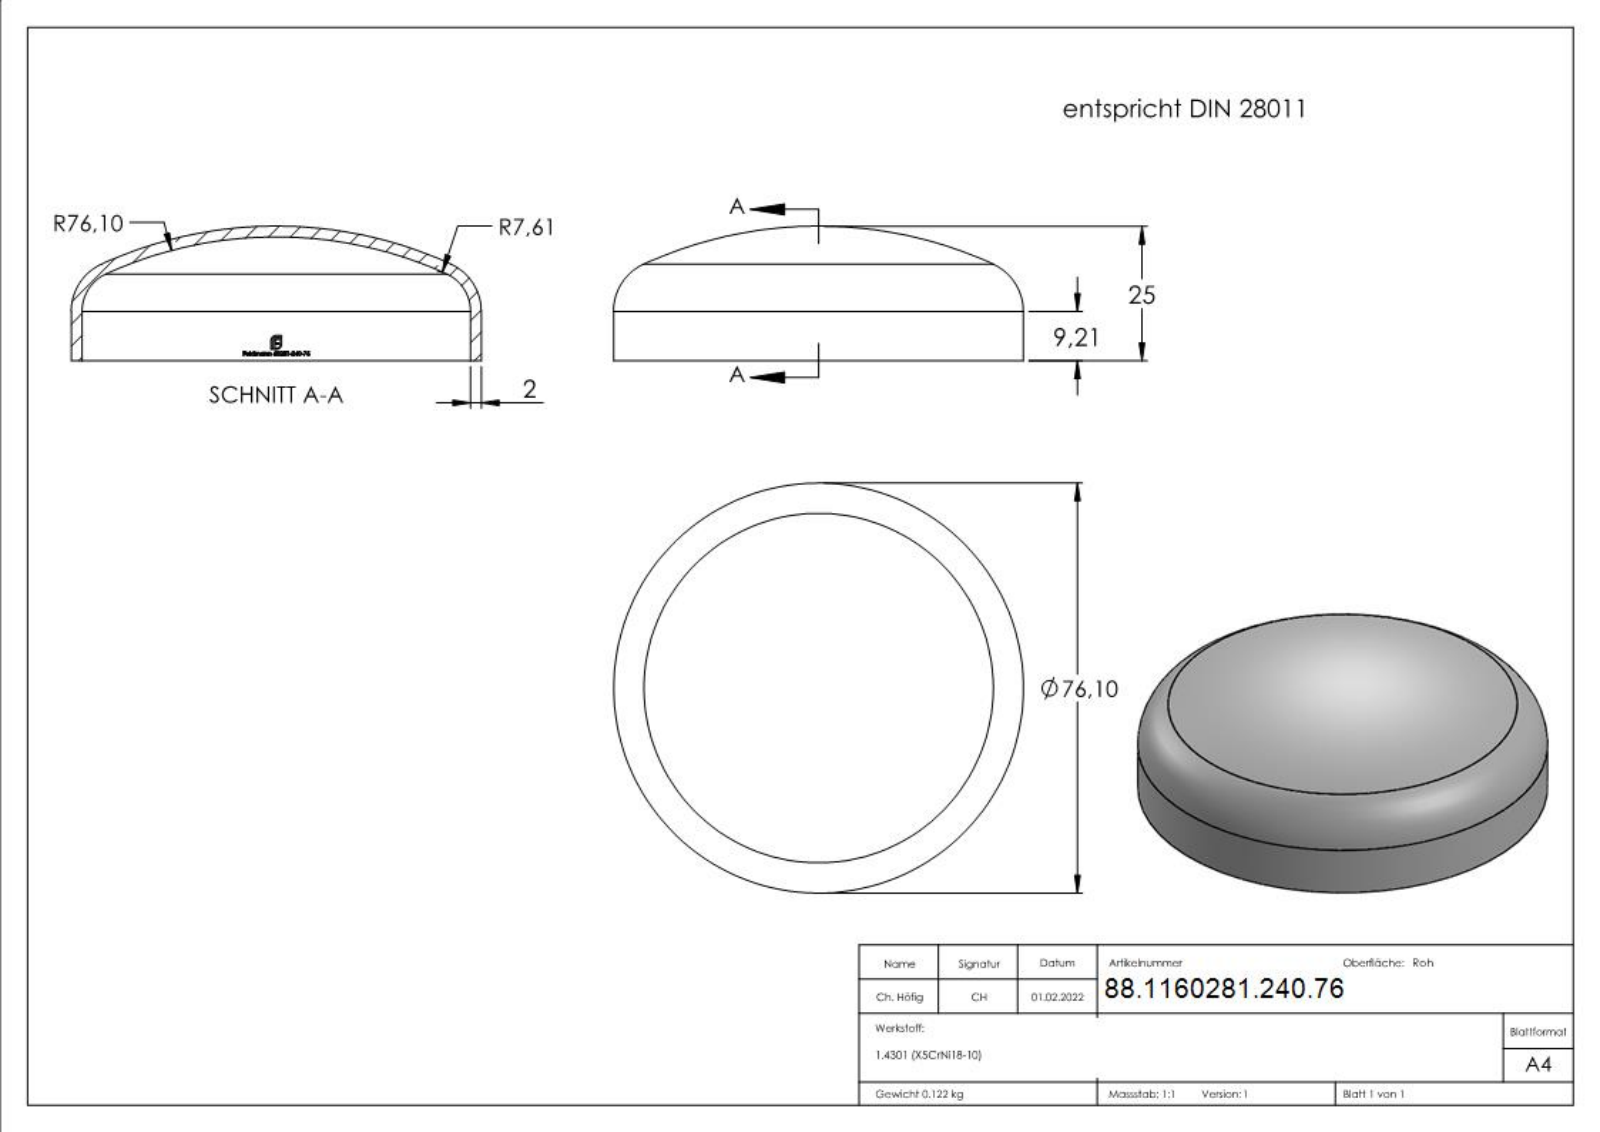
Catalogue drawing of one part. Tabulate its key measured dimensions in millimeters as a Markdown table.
| quantity | value |
| --- | --- |
| part name | 60281-240-76 |
| STEP written by | SolidWorks 2018 (CONFIG_CONTROL_DESIGN) |
| units | millimeters |
| bodies | 1 solid, 311 faces (128 planar, 42 cylindrical, 141 other) |
| overall size | 76.1 × 76.1 × 25 |
| volume | 15 398 mm³ |
| surface area | 15 881 mm² |
| round holes (diameter × count) | 72.1 × 1 |
| round bosses / shafts (diameter × count) | 76.1 × 1 |
| partial cylindrical surfaces (radius × count) | 36.15 × 1 |
| main face-to-face distances | 1.76, 3.37, 1.96, 2.45, 3.12, 1.79, 1, 1.35, 0.49, 2.32 |
